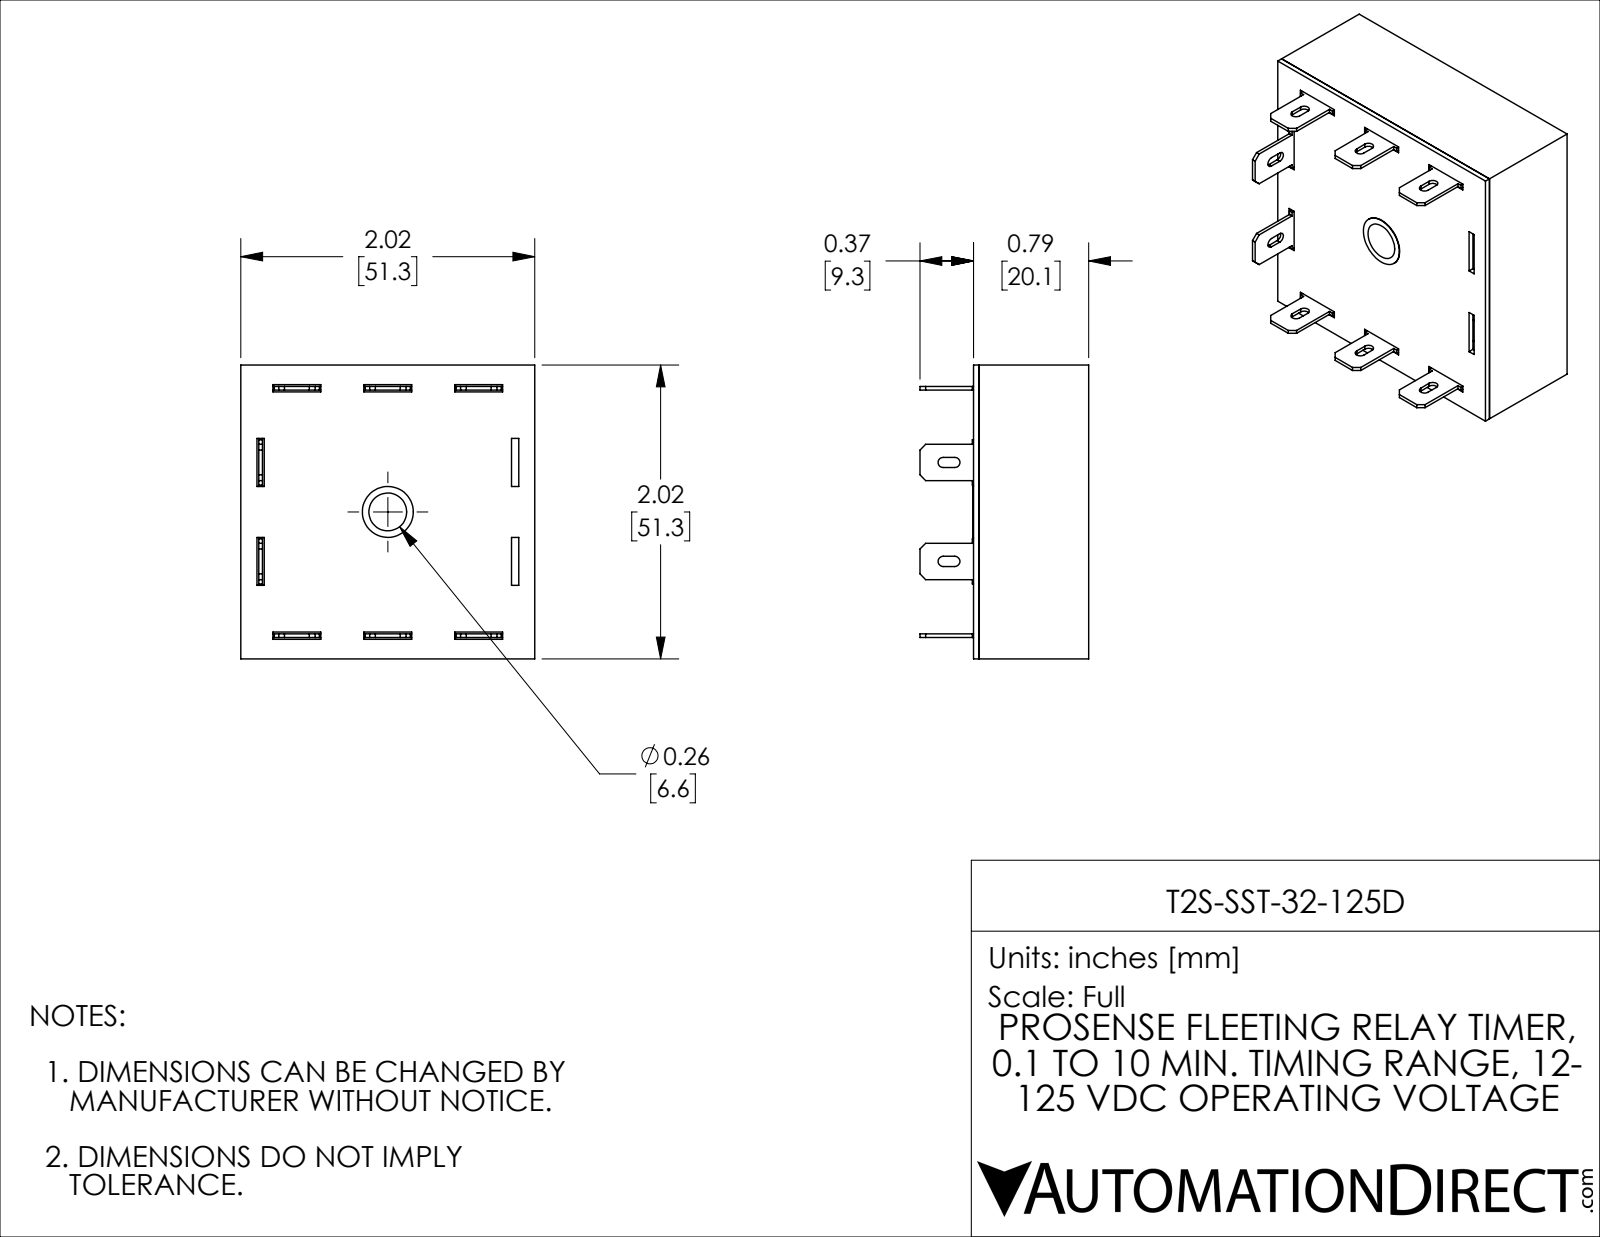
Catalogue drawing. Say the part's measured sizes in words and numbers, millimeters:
The part is named "T2S-SST-32-125D". Its 3-D file was written by "SolidWorks 2021 (CONFIG_CONTROL_DESIGN)". It is 10 solids with 256 faces: 234 planar, 20 cylindrical and 2 other. Overall it measures 51.31 by 51.31 by 29.46 millimeters. Its volume is 11 042 cubic millimeters and its surface area 22 819 square millimeters. Round holes: 1 of diameter 8.89. Partial cylindrical surfaces (rounded edges, fillets, slot ends): 10 of radius 0.89. The main face-to-face distances are 1.14, 50.16, 19.15, 20.12, 0.97, 18.01, 18.98, 51.3, 49.02, 3.74.
